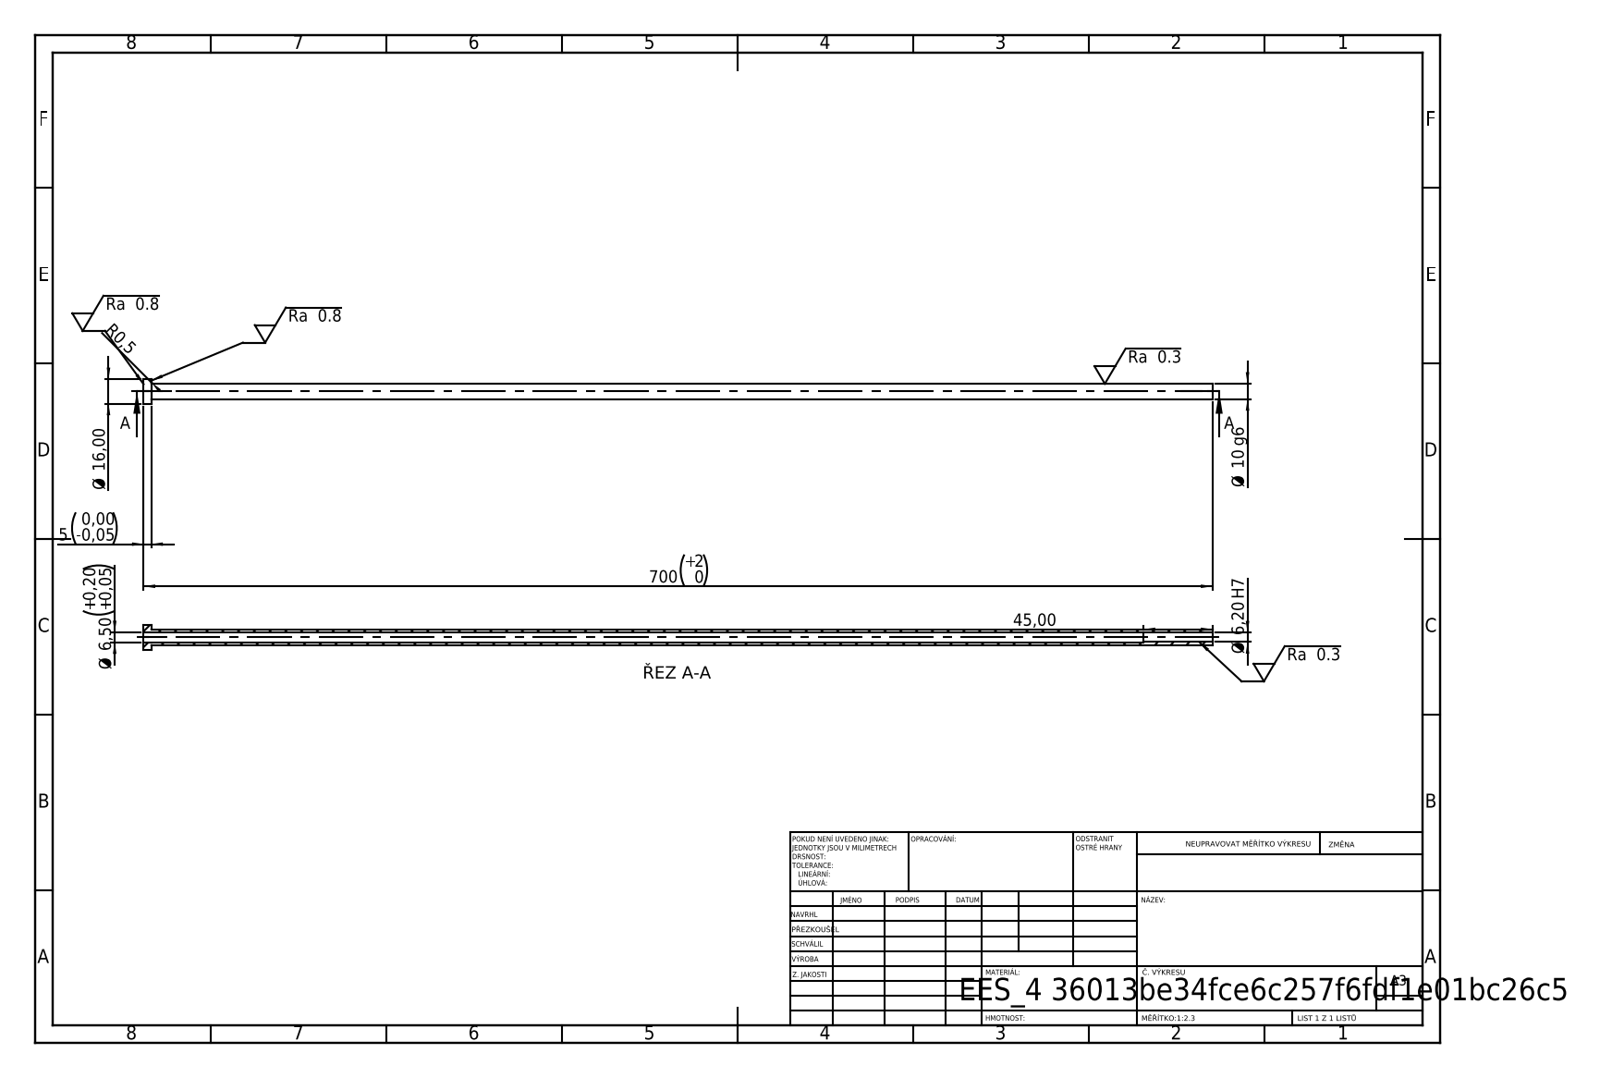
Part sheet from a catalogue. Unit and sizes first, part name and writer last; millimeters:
Units: millimetres
Overall size (bounding box): 700 × 16 × 16
Round holes (diameter × count): ⌀6.2 ×1, ⌀6.5 ×1
Round bosses / shafts (diameter × count): ⌀16 ×1, ⌀10 ×1
Main face-to-face distances: 5, 700, 695, 655, 650, 45
Volume: 32 499 mm³ · Surface area: 36 672 mm²
Bodies: 1 solid, 14 faces (4 planar, 8 cylindrical, 2 other)
STEP written by: SolidWorks 2019 (CONFIG_CONTROL_DESIGN)
